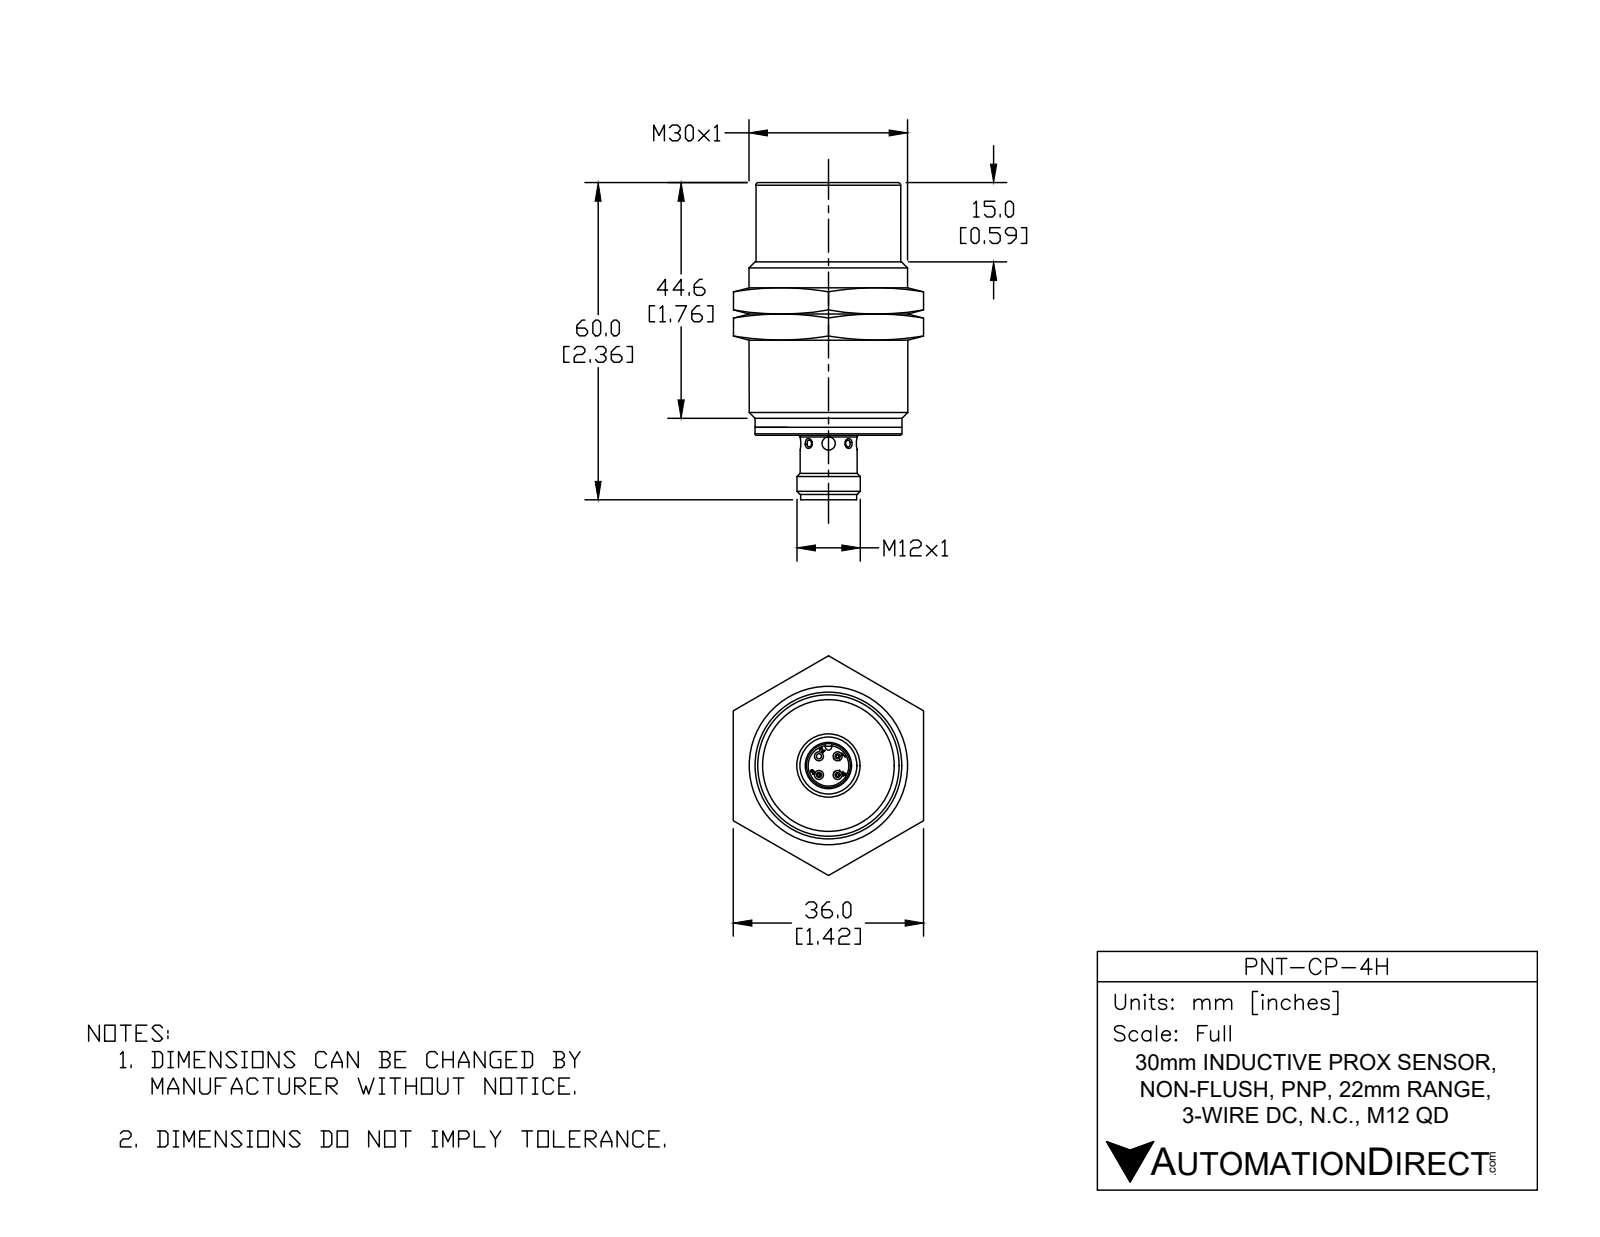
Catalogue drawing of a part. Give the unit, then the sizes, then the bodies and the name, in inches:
Units: inches
Overall size (bounding box): 2.362 × 1.181 × 1.181
Round holes (diameter × count): ⌀0.043 ×3, ⌀0.04 ×2, ⌀0.098 ×2, ⌀0.038 ×1, ⌀0.04 ×1, ⌀0.323 ×1, ⌀0.327 ×1, ⌀0.394 ×1, ⌀1.047 ×1, ⌀1.076 ×1
Round bosses / shafts (diameter × count): ⌀0.039 ×9, ⌀1.181 ×1, ⌀1.094 ×1, ⌀1.083 ×1, ⌀1.074 ×1, ⌀1.044 ×1, ⌀1.037 ×1, ⌀1.021 ×1
Partial cylindrical surfaces — rounded edges, fillets, slot ends (radius × count): R0.004 ×12, R0.02 ×8, R0.157 ×6, R0.03 ×3, R0.039 ×3, R0.024 ×1, R0.031 ×1
Main face-to-face distances: 0.157, 1.882, 1.724, 0.037, 0.12, 1.844, 1.854, 0.13, 0.031, 0.028
Hole centre spacings: 0.098, 0.139, 0.197
Volume: 1.934 in³ · Surface area: 25.17 in²
Bodies: 1 solid, 660 faces (260 planar, 164 cylindrical, 236 other)
Part name (STEP PRODUCT): PNT-CP-4H
STEP written by: SolidWorks 2017 (AUTOMOTIVE_DESIGN)
